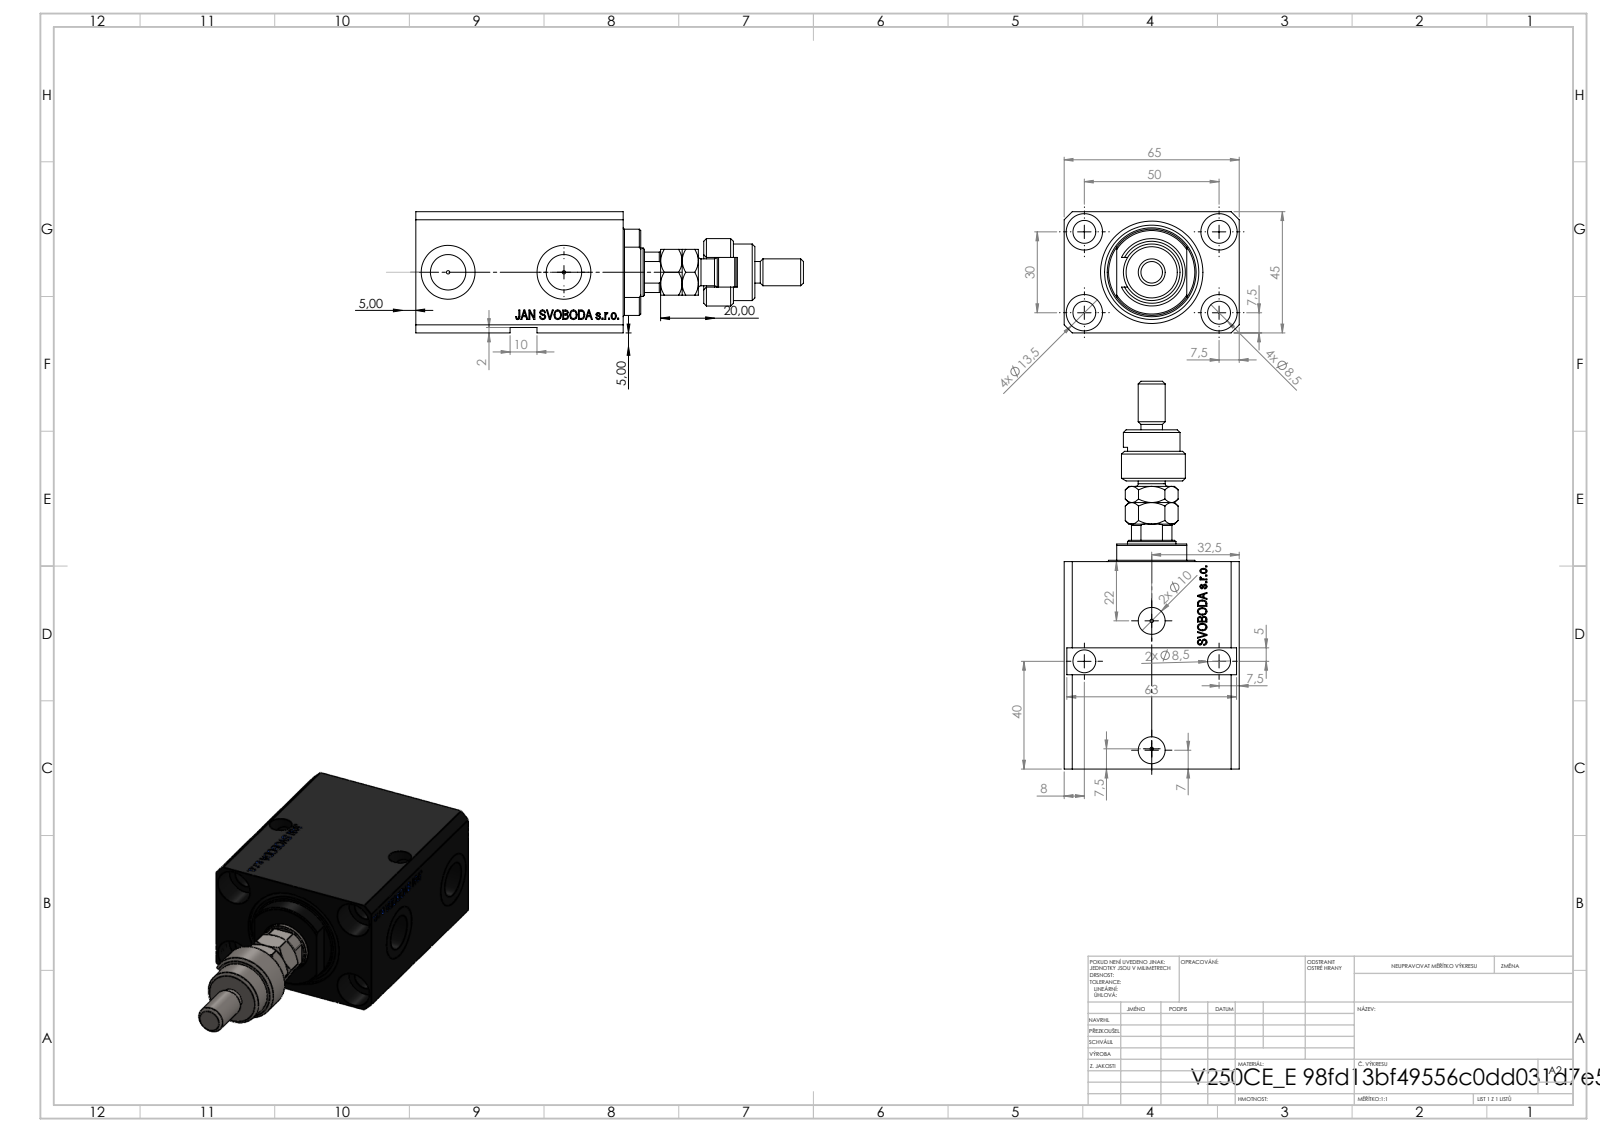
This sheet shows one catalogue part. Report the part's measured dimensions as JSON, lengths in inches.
{"part_name": "V250CE_E_Body; MFA; V250CE_C_VCP; FEMALE_PART_FOR_DFA (+1 more)", "step_written_by": "SolidWorks 2019 (CONFIG_CONTROL_DESIGN)", "units": "inches", "bodies": {"solids": 5, "faces": 998, "planar": 467, "cylindrical": 109, "other": 422}, "overall_size": [5.669, 2.559, 1.772], "volume_in3": 12.2, "surface_area_in2": 91.2, "round_holes": [[0.335, 7], [0.049, 4], [0.531, 4], [0.394, 2], [0.518, 2], [0.787, 2], [0.709, 1], [1.496, 1]], "round_bosses_or_shafts": [[0.984, 1], [0.827, 1], [0.63, 1], [0.394, 1], [0.315, 1]], "partial_cylinders_radius": [[0.217, 1], [0.335, 1], [0.344, 1], [0.63, 1]], "face_to_face_distances": [1.772, 0.551, 2.559, 2.48, 3.031, 0.272, 2.209, 2.76, 1.102, 0.079], "hole_center_spacings": [1.148, 1.969, 1.181, 1.613, 1.63, 2.296, 0.021, 1.693]}
